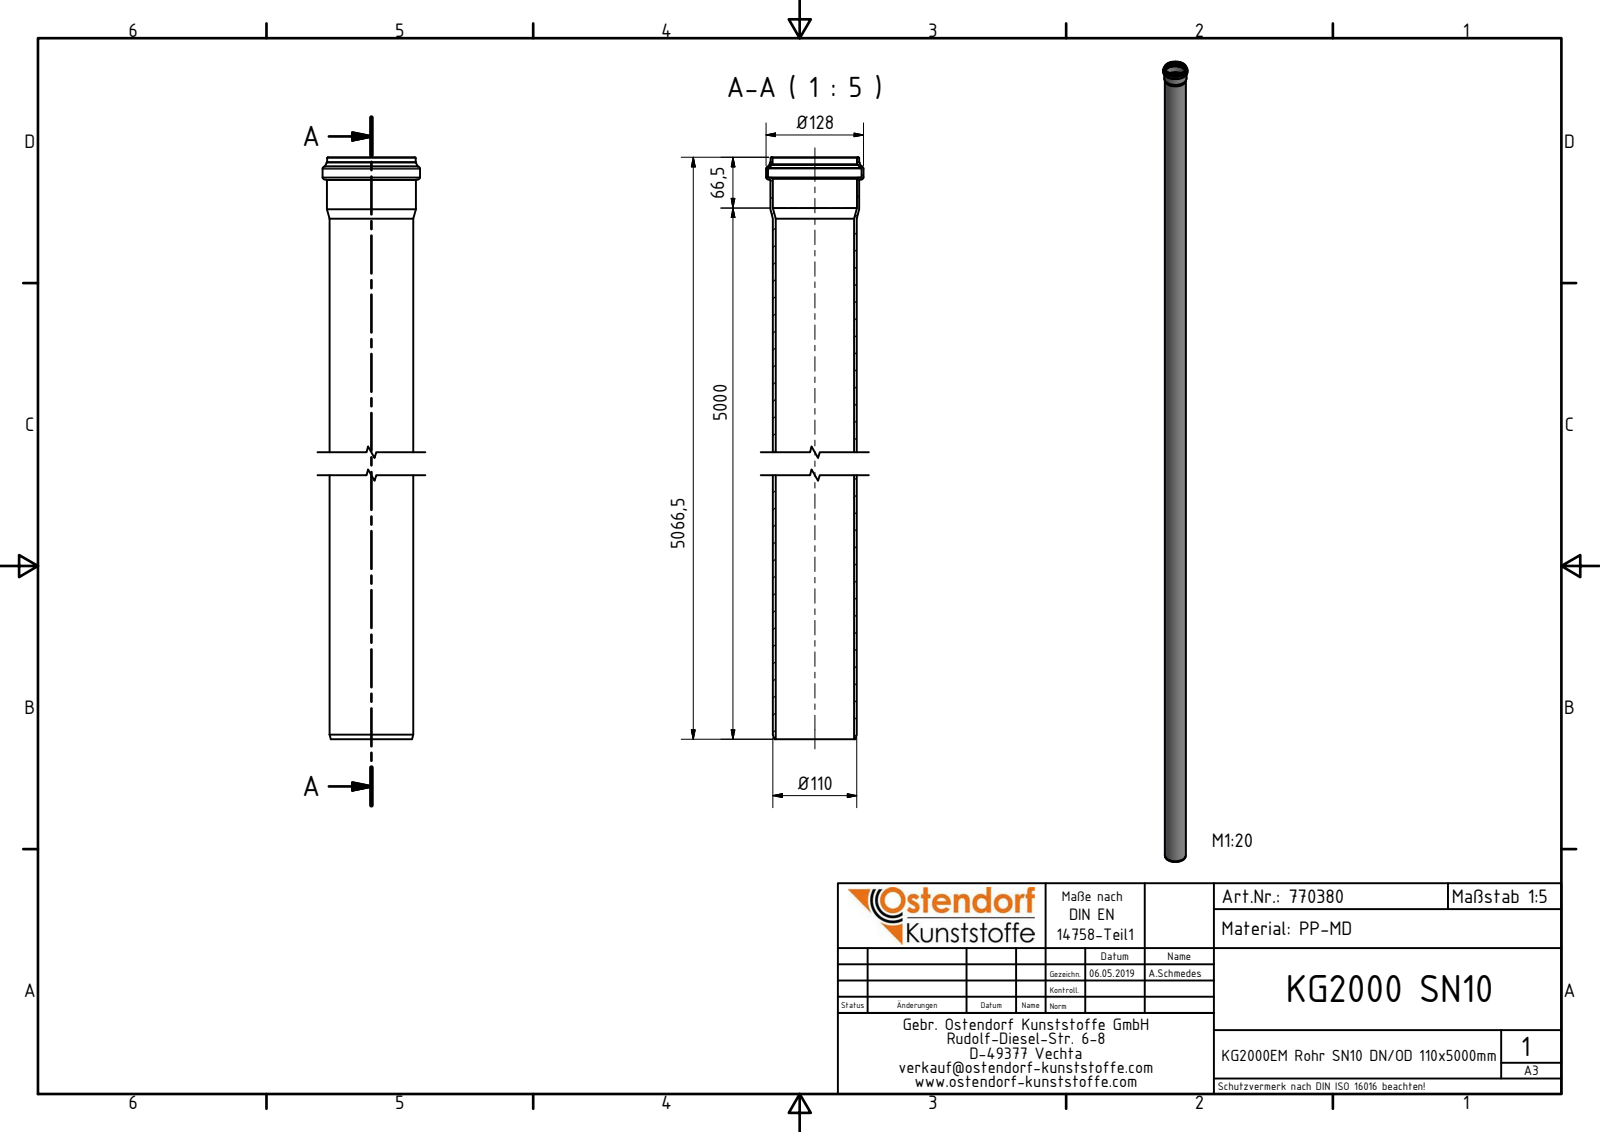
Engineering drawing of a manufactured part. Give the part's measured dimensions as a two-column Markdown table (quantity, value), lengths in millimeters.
| quantity | value |
| --- | --- |
| part name | 770380 KG2000EM Rohr SN10 DN-OD110x5000 |
| STEP written by | Autodesk Inventor 2016 (AUTOMOTIVE_DESIGN) |
| units | millimeters |
| bodies | 1 solid, 37 faces (6 planar, 9 cylindrical, 22 other) |
| overall size | 5066.5 × 128 × 128 |
| volume | 5 964 000 mm³ |
| surface area | 3 402 000 mm² |
| round holes (diameter × count) | 102.96 × 1, 110.5 × 1, 110.9 × 1, 122.8 × 1 |
| round bosses / shafts (diameter × count) | 128 × 1, 116.7 × 1, 116.1 × 1, 110 × 1 |
| main face-to-face distances | 5037.4, 5066.5, 29.1, 5038.22, 0.82, 28.28, 5054.5, 17.1, 16.28, 12 |
